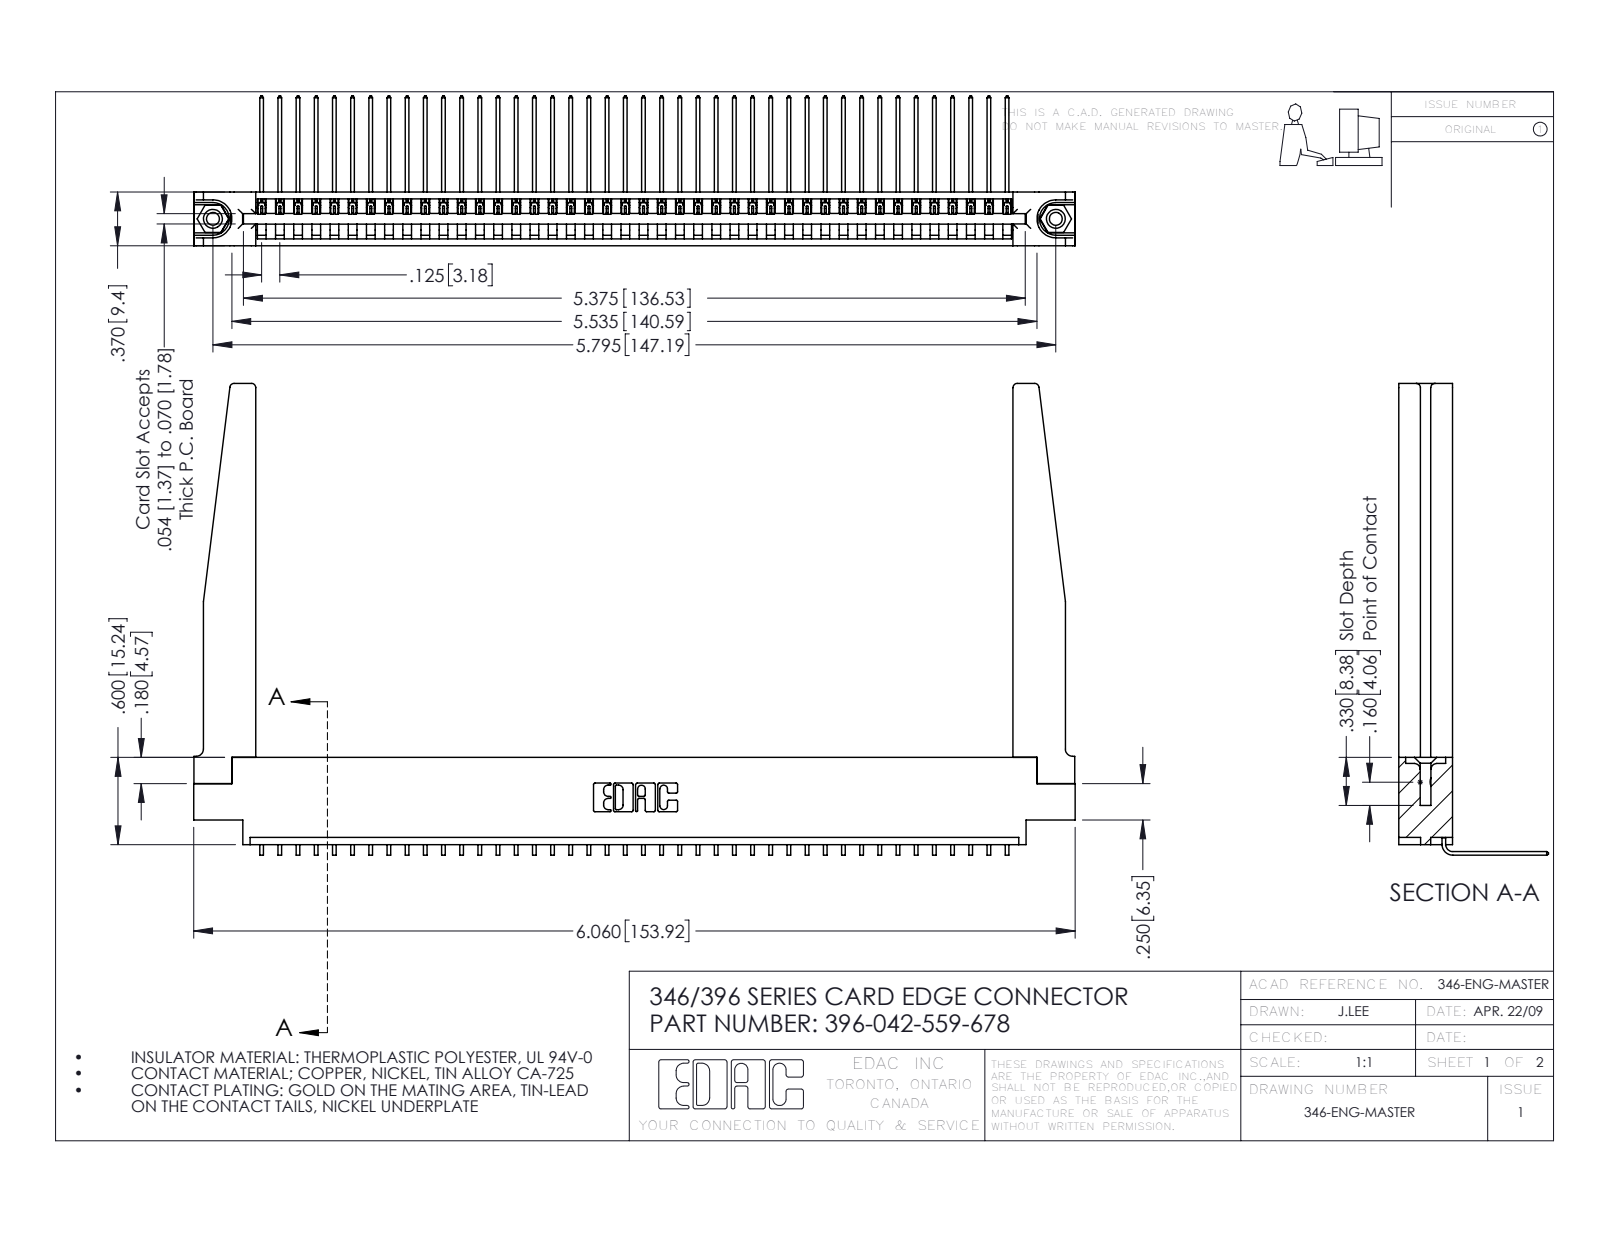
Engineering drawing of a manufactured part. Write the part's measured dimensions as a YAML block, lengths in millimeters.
part_name: "396-042-559-678; 345-250-001_345-250-001-102; 346-220-078_345-220-078; 346 Part_0.170 Offset - 0.156 Dia-TH (+1 more)"
step_written_by: "SolidWorks 2016 (CONFIG_CONTROL_DESIGN)"
units: millimeters
bodies: {solids: 47, faces: 2880, planar: 1986, cylindrical: 842, other: 52}
overall_size: [153.9, 82.4, 26.2]
volume: 21630
surface_area: 25940
round_holes:
  - {diameter: 2.3, count: 2}
  - {diameter: 3.2, count: 2}
  - {diameter: 4, count: 2}
  - {diameter: 1.6, count: 1}
round_bosses_or_shafts:
  - {diameter: 3.9, count: 2}
partial_cylinders:
  - {radius: 0.2, count: 84}
  - {radius: 0.3, count: 22}
  - {radius: 0.8, count: 8}
  - {radius: 0.2, count: 6}
  - {radius: 0.8, count: 6}
  - {radius: 0.7, count: 3}
  - {radius: 1.3, count: 3}
  - {radius: 0.8, count: 2}
face_to_face_distances: [9.4, 1.2, 8.2, 1.8, 3.8, 3.8, 0.6, 6.4, 7.6, 5.6]
hole_center_spacings: [6.2, 141.9, 147.2]
